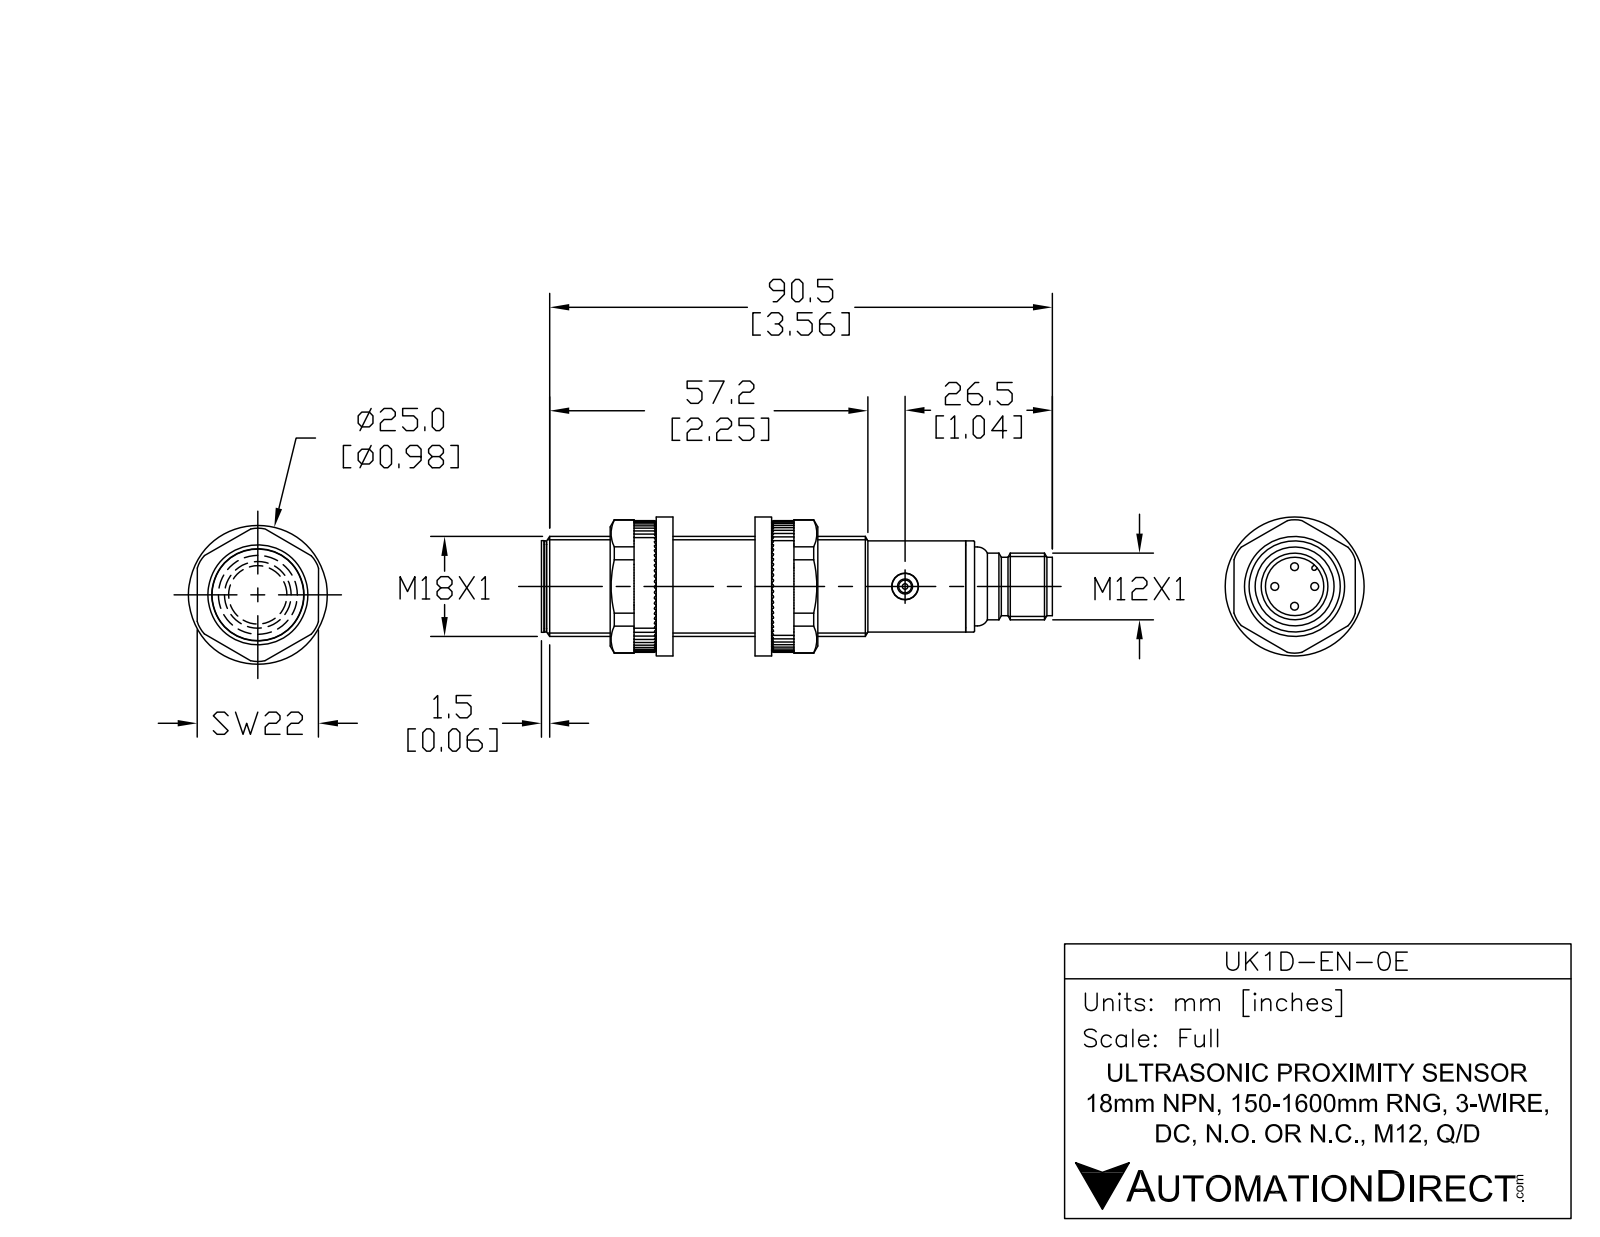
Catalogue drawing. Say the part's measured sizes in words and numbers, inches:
The part is named "UK1D-EN-0E". Its 3-D file was written by "SolidWorks 2017 (AUTOMOTIVE_DESIGN)". It is 6 solids with 106 faces: 21 planar, 48 cylindrical and 37 other. Overall it measures 3.606 by 0.709 by 0.709 inches. Its volume is 1.202 cubic inches and its surface area 10.68 square inches. Round holes: 1 of diameter 0.106, 1 of diameter 0.185, 1 of diameter 0.276, 1 of diameter 0.327, 1 of diameter 0.374. Round bosses or shafts: 4 of diameter 0.039, 1 of diameter 0.709, 1 of diameter 0.654, 1 of diameter 0.646, 1 of diameter 0.622, 1 of diameter 0.559, 1 of diameter 0.472, 1 of diameter 0.413. Partial cylindrical surfaces (rounded edges, fillets, slot ends): 1 of radius 0.024. The main face-to-face distances are 2.957, 0.039, 2.996, 0.037, 2.994, 0.043, 0.157, 3.055, 3.053, 3.016.
